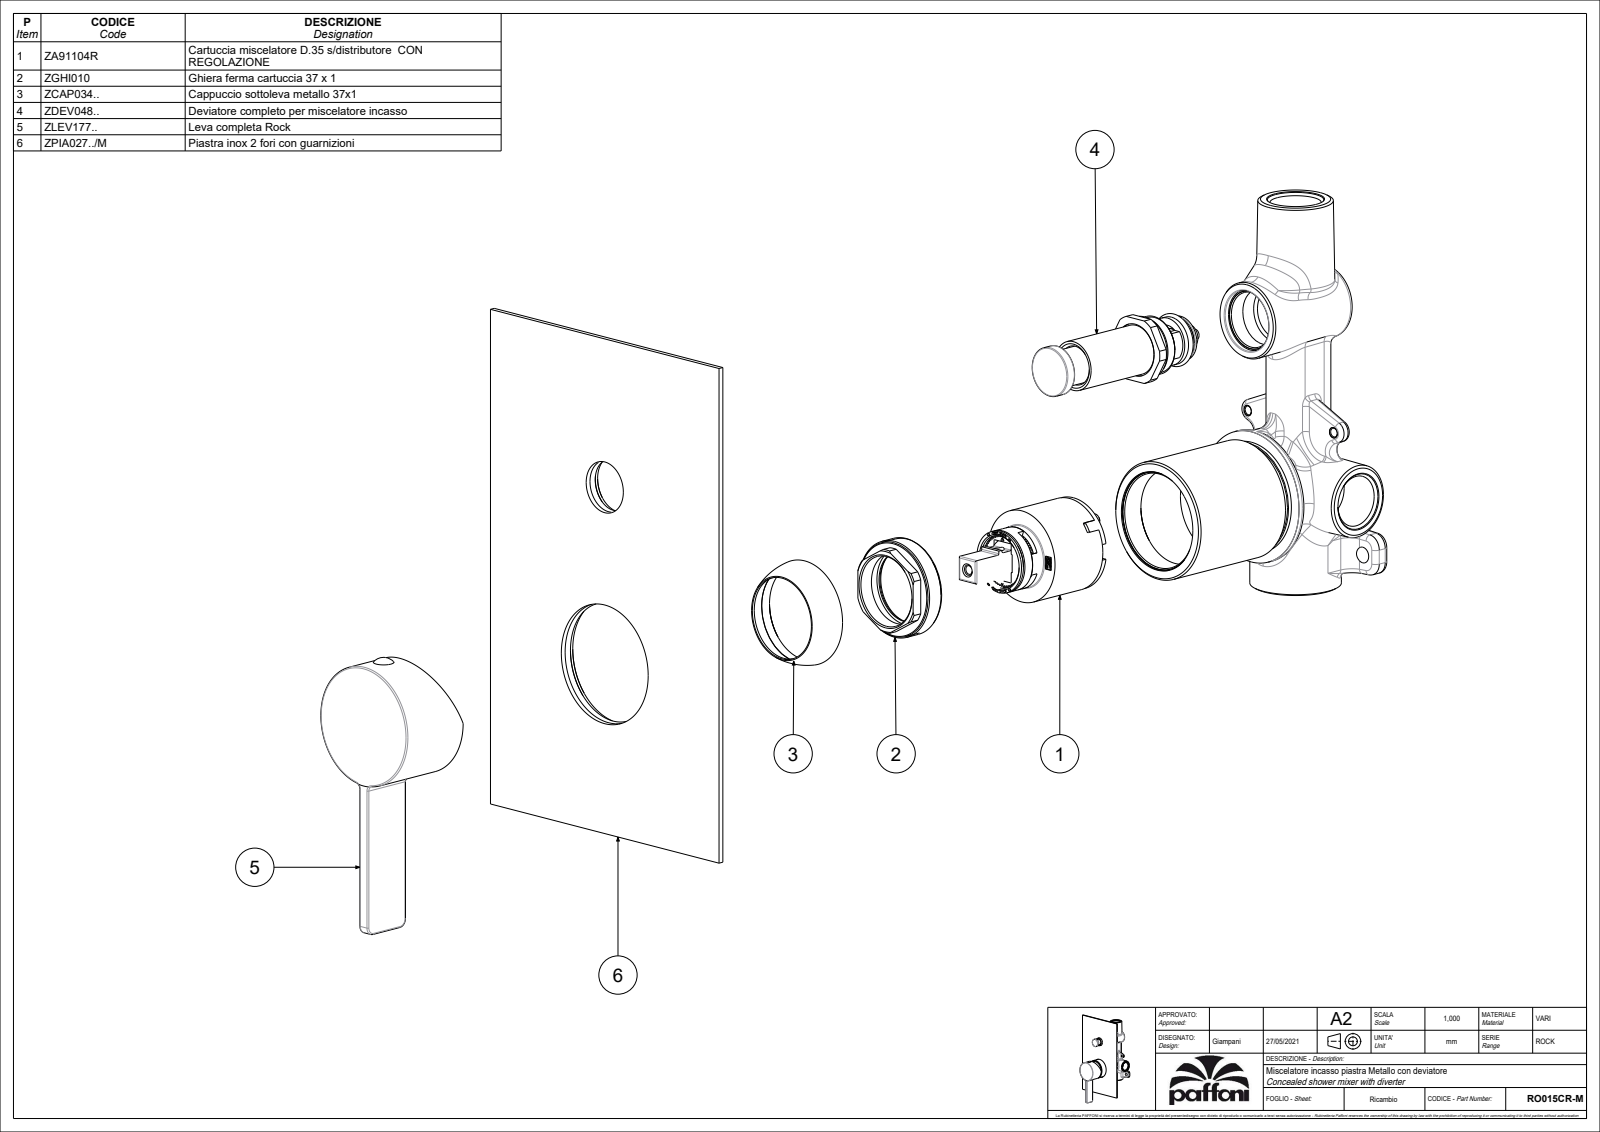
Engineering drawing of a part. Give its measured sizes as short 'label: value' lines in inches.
name: RO015CR-M
written by: CREO PARAMETRIC BY PTC INC, 2020044 (CONFIG_CONTROL_DESIGN)
unit: in
bodies: 0 solids, 66 faces (18 planar, 20 cylindrical, 28 other)
size: 8.071 × 4.724 × 1.933
bosses: 1× ⌀1.791, 1× ⌀1.764, 1× ⌀0.736, 1× ⌀0.732, 1× ⌀0.551
rounds: 6× R0.02, 2× R0.079, 2× R0.118
face distances: 0.079, 0.591, 0.669, 0.177, 2.274, 2.451, 4.724, 0.236, 0.157, 0.433
